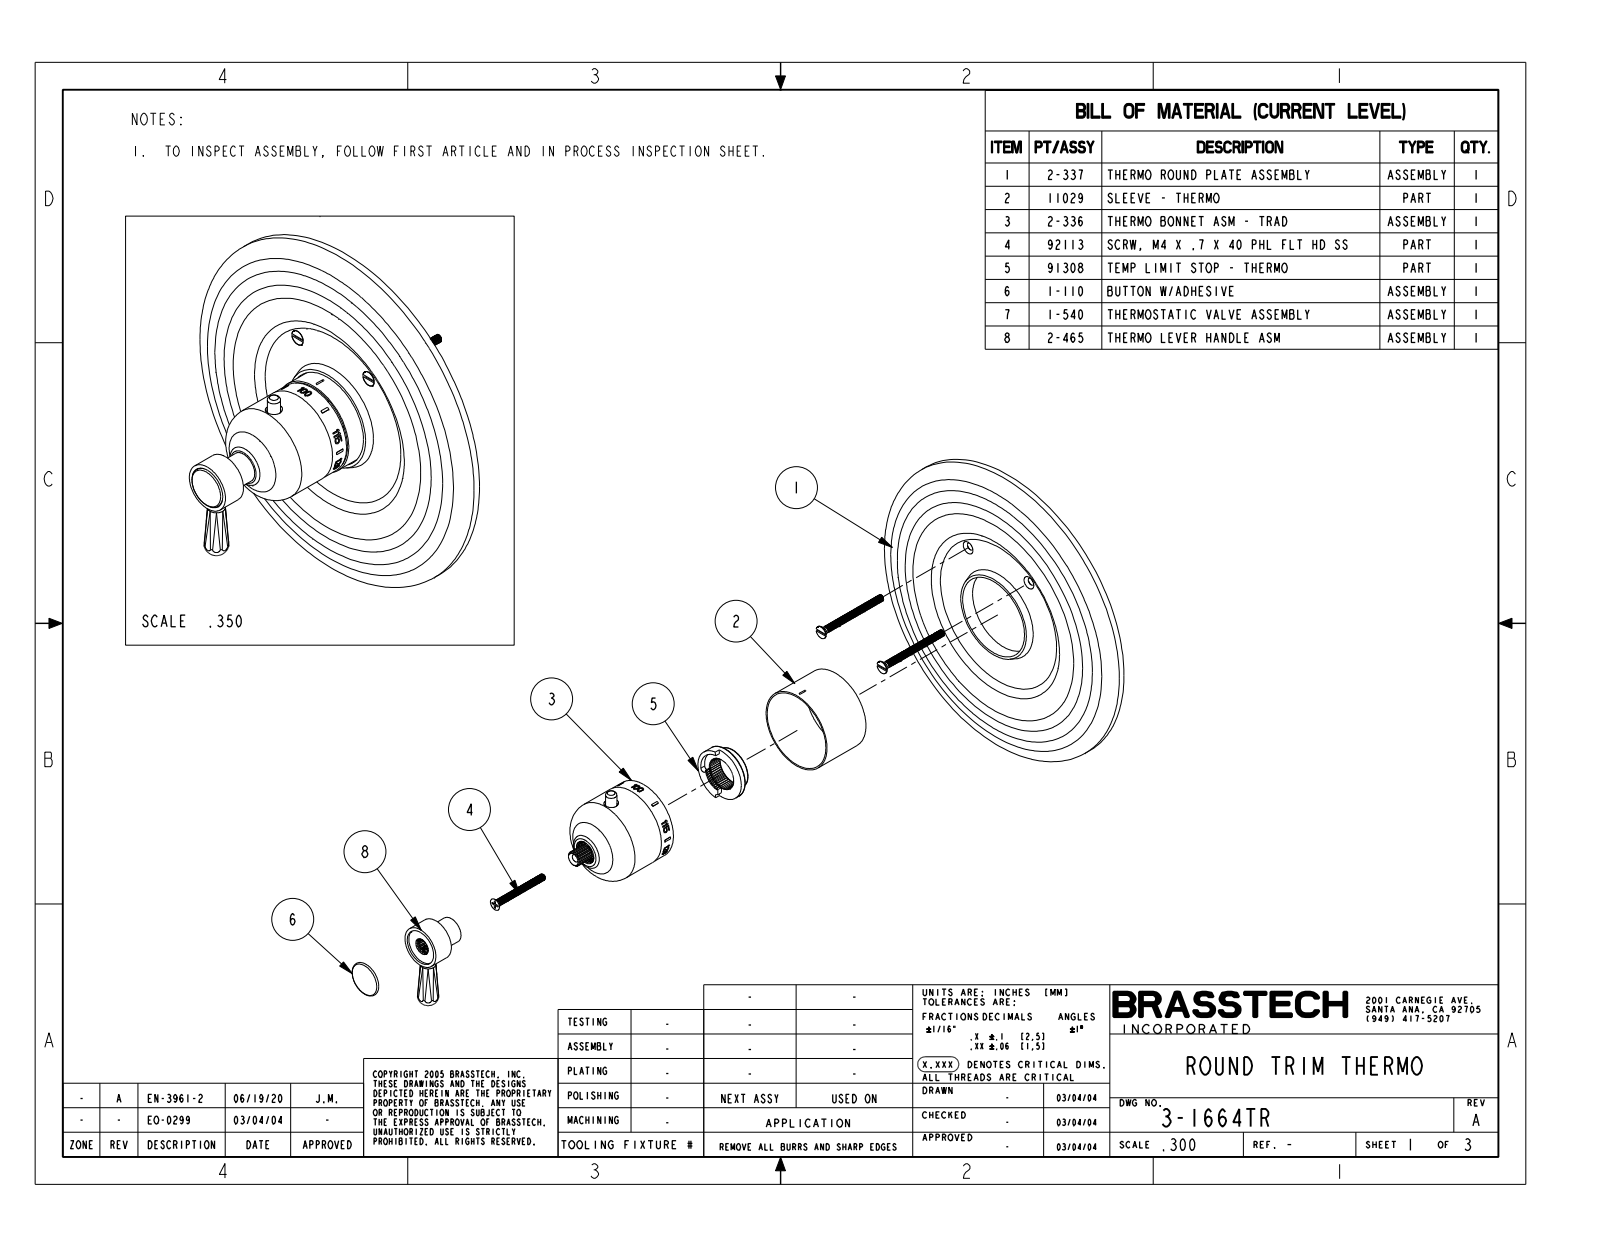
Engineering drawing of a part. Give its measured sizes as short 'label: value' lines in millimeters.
name: 3-1664TR
written by: CREO PARAMETRIC BY PTC INC, 2018400 (CONFIG_CONTROL_DESIGN)
unit: mm
bodies: 1 solid, 418 faces (337 planar, 39 cylindrical, 42 other)
size: 190.5 × 190.5 × 98.5
volume: 412 100 mm³; area: 74 580 mm²
holes: 1× ⌀9.2
bosses: 1× ⌀190.5, 1× ⌀50, 1× ⌀49.3, 1× ⌀49, 1× ⌀25.4, 1× ⌀15.9, 1× ⌀8.9, 1× ⌀6.6
rounds: 1× R24.6
face distances: 8, 4, 12, 95.4, 87.5, 83.4, 21.9, 14, 9.9, 73.5
